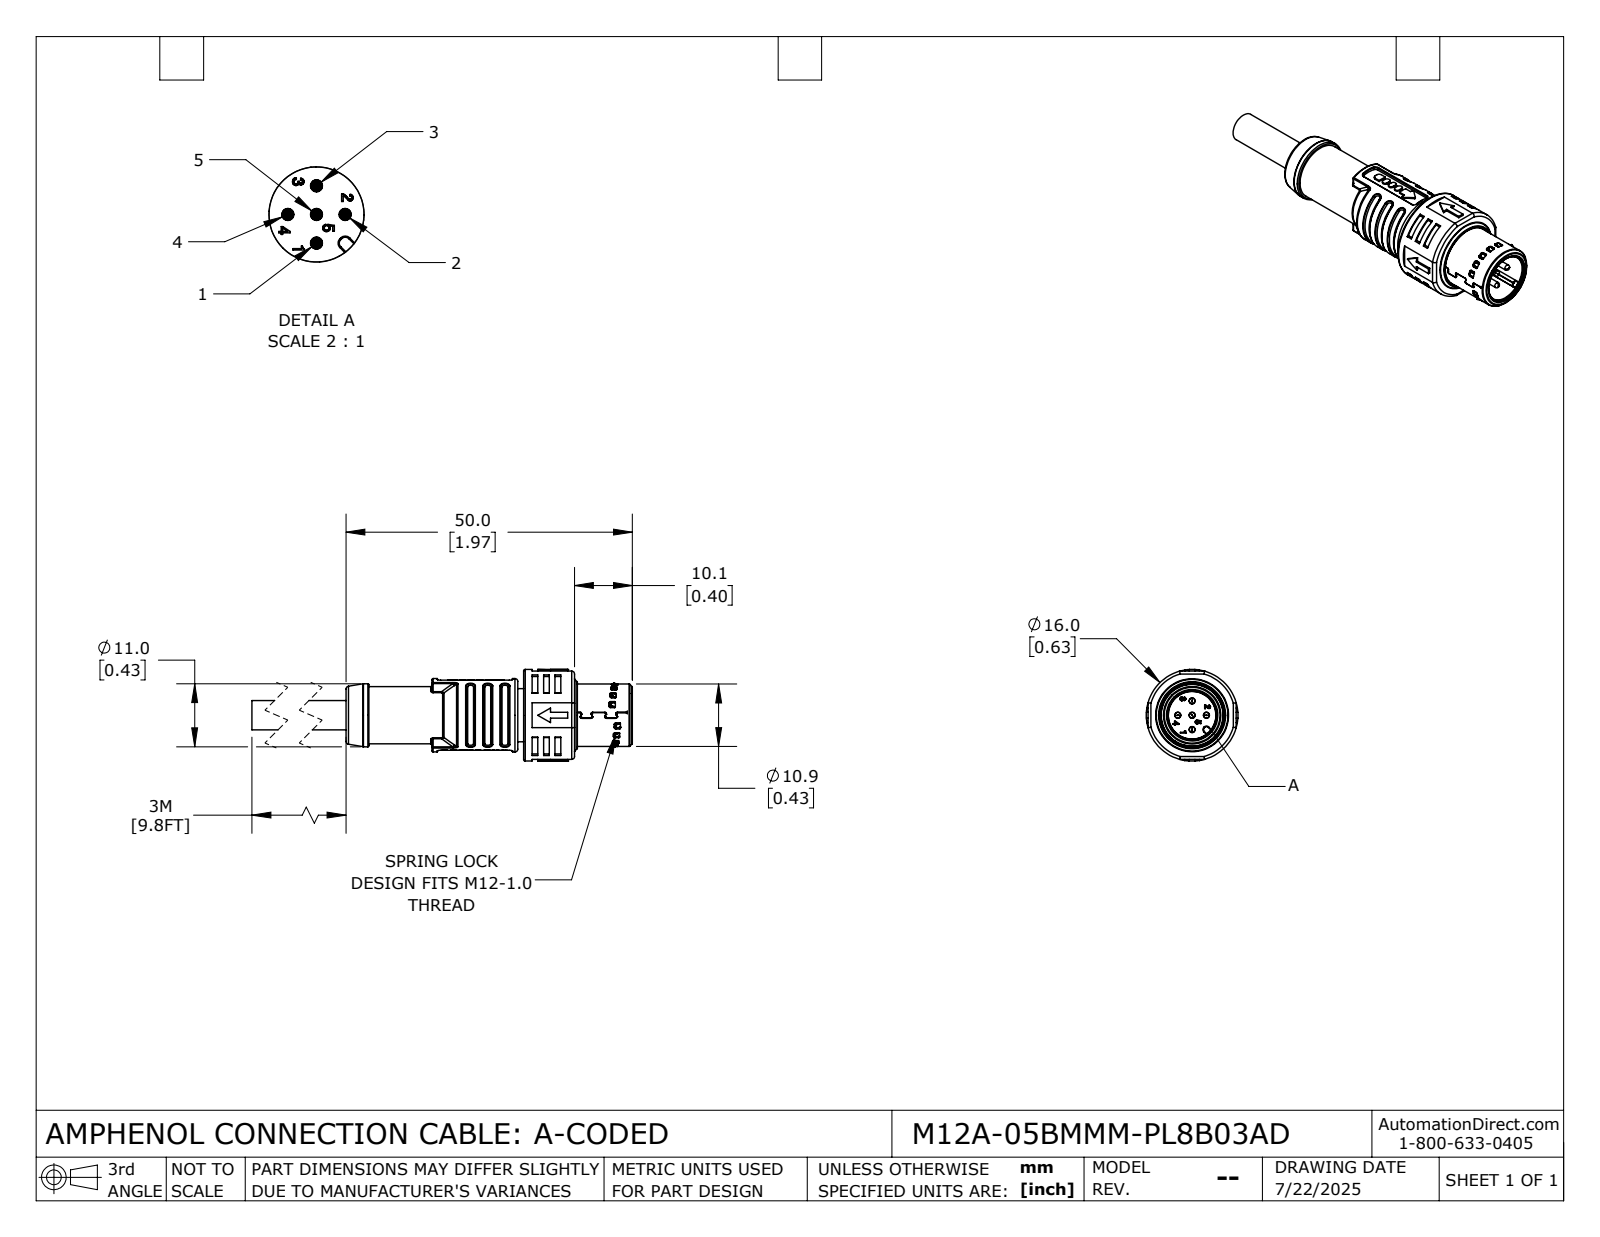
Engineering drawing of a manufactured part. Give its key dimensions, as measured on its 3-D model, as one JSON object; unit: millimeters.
{"part_name": "M12A-05BMMM-PL8B03AD", "step_written_by": "SolidWorks 2024 (CONFIG_CONTROL_DESIGN)", "units": "millimeters", "bodies": {"solids": 1, "faces": 2230, "planar": 1085, "cylindrical": 648, "other": 497}, "overall_size": [65, 16, 16], "volume_mm3": 5076, "surface_area_mm2": 5586, "round_holes": [[1.05, 5], [8.3, 1], [9, 1], [10.15, 1], [10.5, 1], [10.9, 1], [11.5, 1], [11.8, 1], [14.2, 1]], "round_bosses_or_shafts": [[1, 5], [16, 1], [14.1, 1], [12.8, 1], [12.4, 1], [11, 1], [10.45, 1], [10.4, 1]], "partial_cylinders_radius": [[0.2, 114], [0.25, 66], [0.3, 64], [0.15, 44], [0.5, 38], [0.13, 12], [0.7, 11], [0.1, 10]], "face_to_face_distances": [1, 10.1, 8.9, 8.6, 2.5, 30, 1.5, 1.2, 32.5, 15.4], "hole_center_spacings": [2.5, 3.54, 5]}
